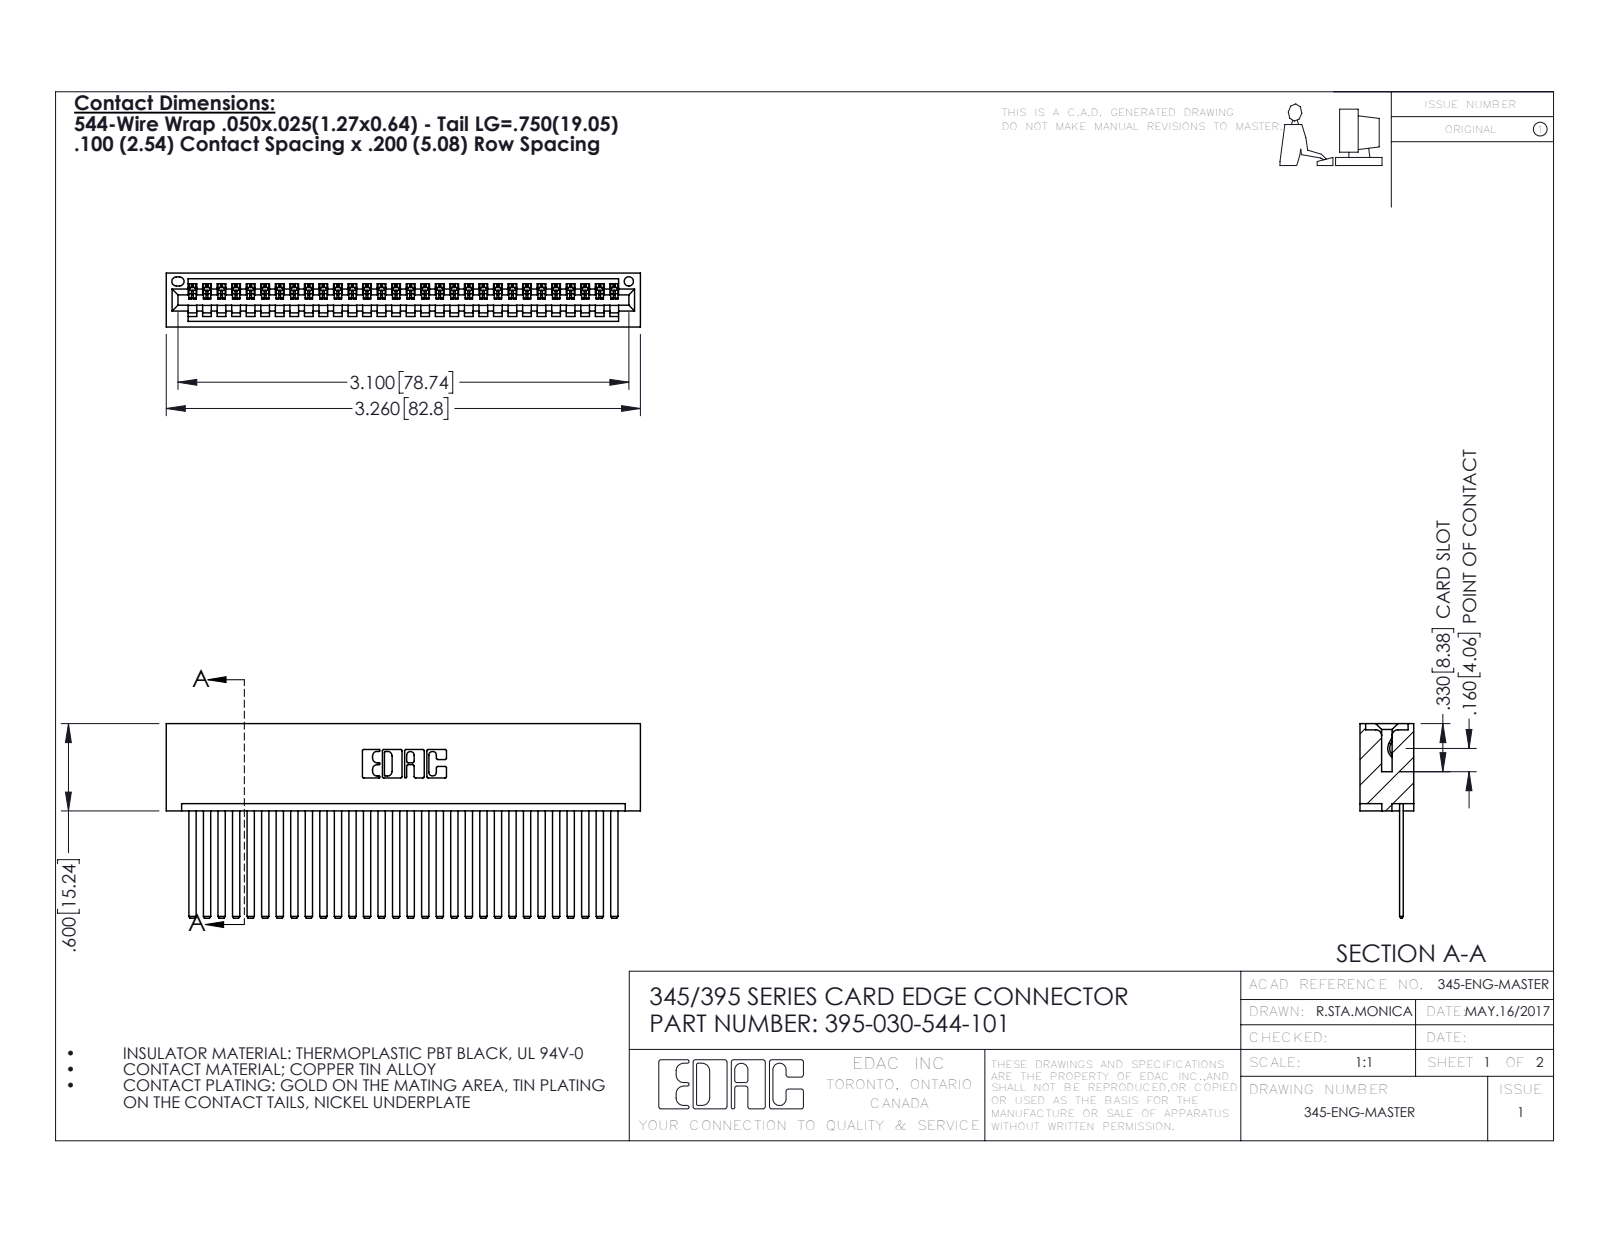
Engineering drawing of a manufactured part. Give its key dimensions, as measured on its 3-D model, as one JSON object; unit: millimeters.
{"part_name": "345-292-001_345-293-144; 345 Part_No Mounting Lugs; 395-030-544-101", "step_written_by": "SolidWorks 2016 (CONFIG_CONTROL_DESIGN)", "units": "millimeters", "bodies": {"solids": 31, "faces": 1678, "planar": 1156, "cylindrical": 522, "other": 0}, "overall_size": [82.8, 34, 9.4], "volume_mm3": 8700, "surface_area_mm2": 12630, "round_holes": [[1.6, 1]], "partial_cylinders_radius": [[0.2, 60], [0.3, 22], [0.2, 6], [0.8, 6], [0.7, 3], [0.8, 2], [1, 2], [0.4, 1]], "face_to_face_distances": [1.8, 7.6, 0.6, 2.5, 6.9, 5.1, 9.4, 5.7, 3.8, 1.8]}
